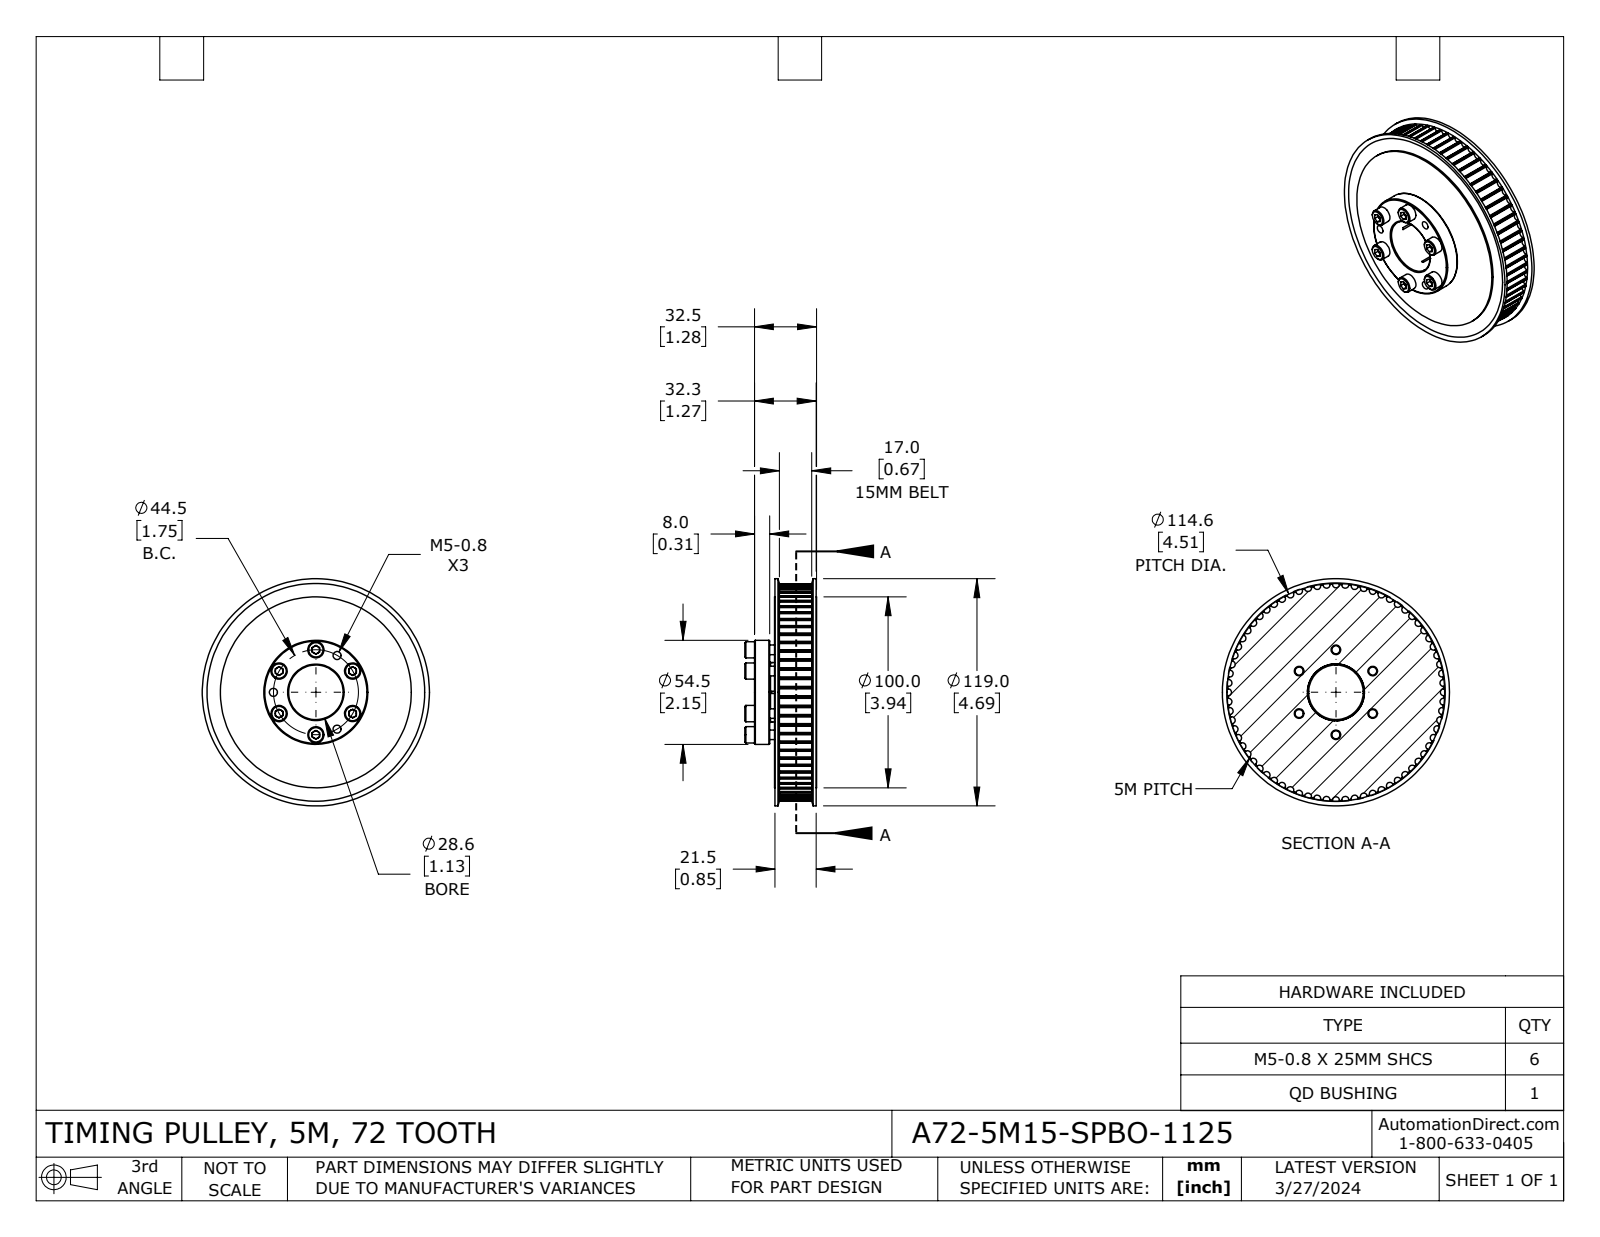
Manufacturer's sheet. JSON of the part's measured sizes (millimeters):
{"part_name": "A72-5M15-SPBO-1125", "step_written_by": "SolidWorks 2021 (CONFIG_CONTROL_DESIGN)", "units": "millimeters", "bodies": {"solids": 10, "faces": 613, "planar": 116, "cylindrical": 435, "other": 62}, "overall_size": [119, 119, 37.5], "volume_mm3": 214949, "surface_area_mm2": 60247, "round_holes": [[4.2, 9], [5.5, 6], [28.57, 1], [28.58, 1], [31.18, 1], [100, 1]], "round_bosses_or_shafts": [[8.5, 6], [5, 6], [119, 1], [54.5, 1], [31.17, 1]], "partial_cylinders_radius": [[0.3, 144], [1.82, 72], [56.73, 1]], "face_to_face_distances": [2.5, 19.5, 22, 0.9, 21.1, 1.6, 18.6, 17, 20.2, 13], "hole_center_spacings": [22.25, 38.54, 11.52, 31.47, 42.99, 38.53, 11.51, 31.46]}
